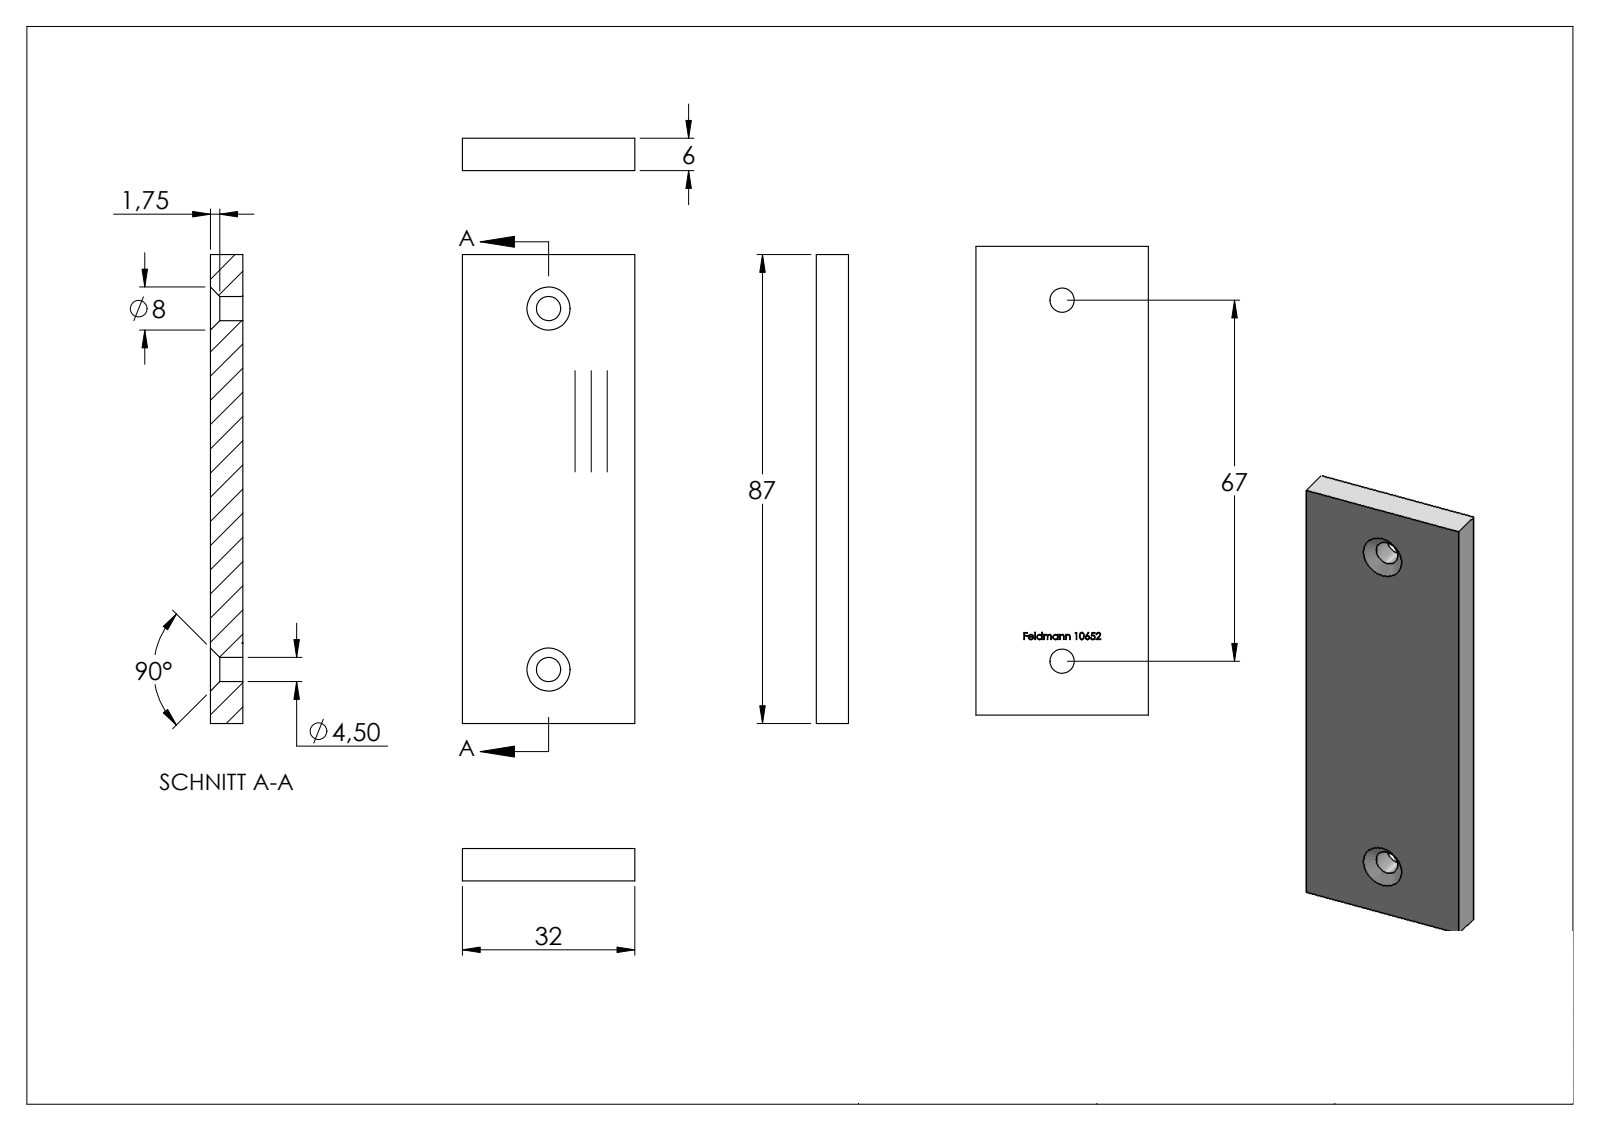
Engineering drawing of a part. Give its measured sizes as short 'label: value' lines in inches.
name: 10652
written by: SolidWorks 2015 (CONFIG_CONTROL_DESIGN)
unit: in
bodies: 1 solid, 187 faces (99 planar, 4 cylindrical, 84 other)
size: 3.425 × 1.26 × 0.236
volume: 1.004 in³; area: 10.99 in²
holes: 2× ⌀0.177
face distances: 0.236, 1.26, 3.425, 0.232, 0.015, 0.117, 0.302, 0.08, 0.551, 2.874
hole spacings: 2.638
